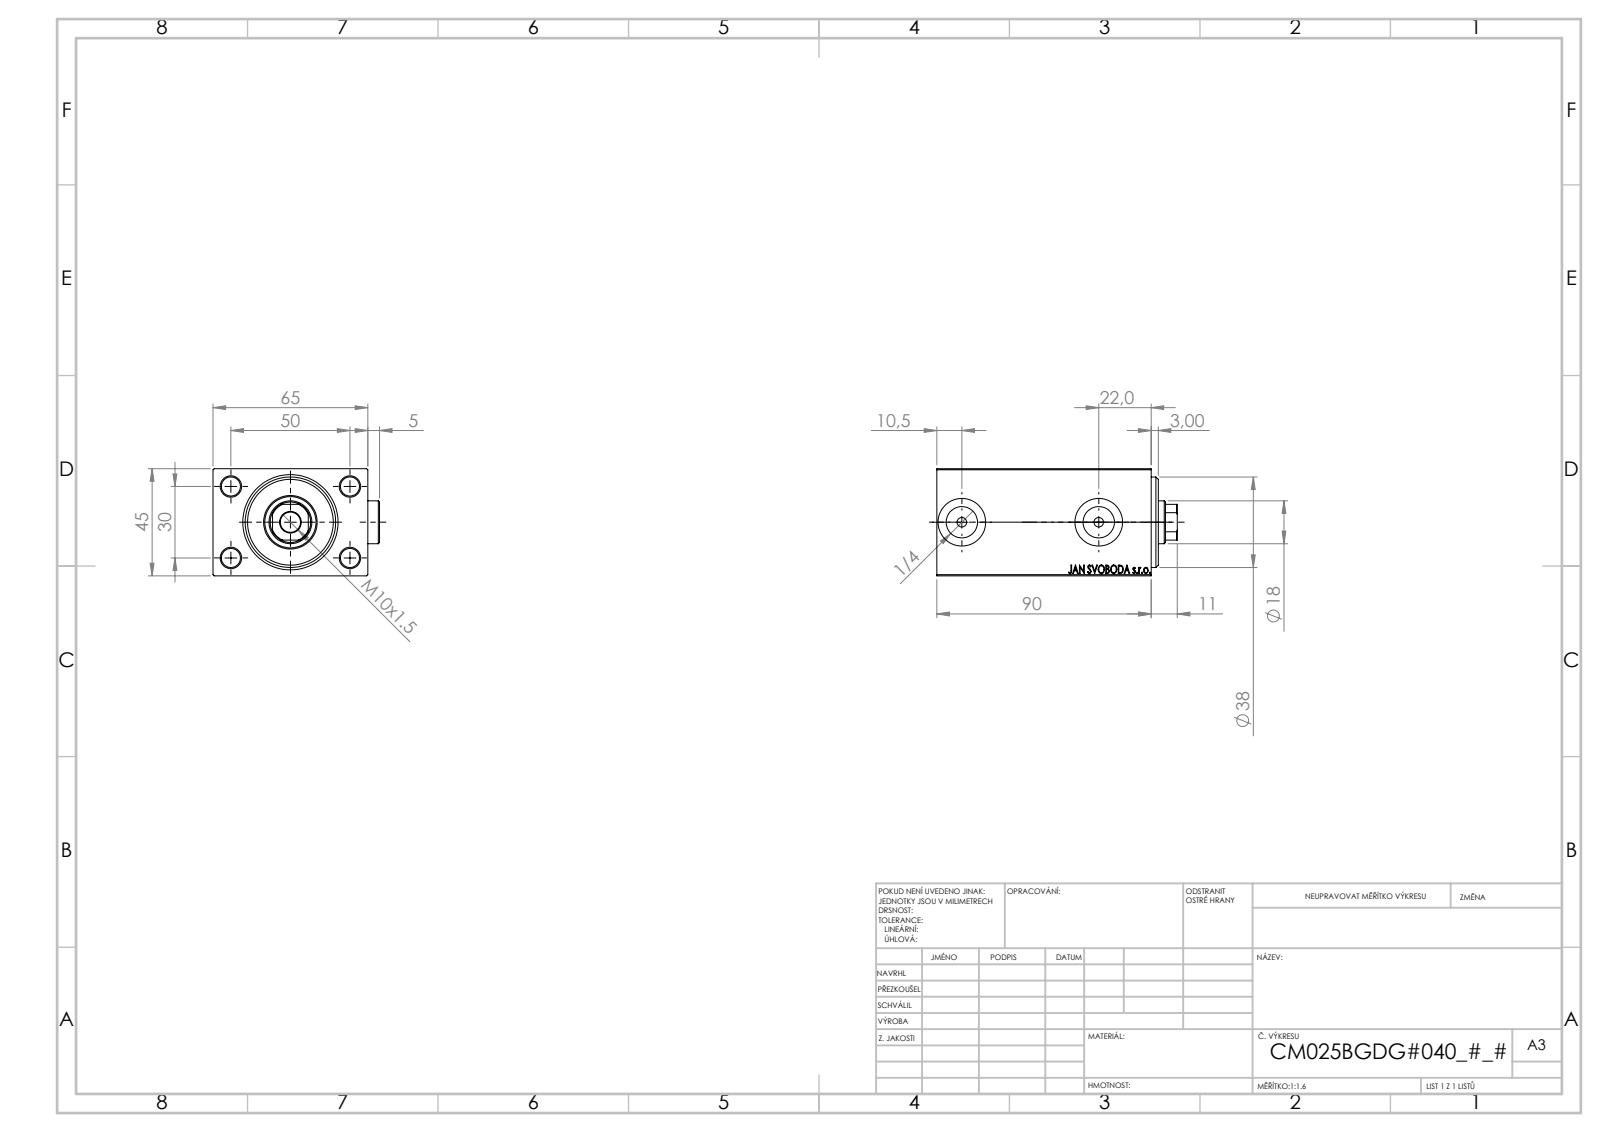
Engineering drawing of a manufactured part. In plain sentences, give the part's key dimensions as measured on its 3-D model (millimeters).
The part is named "Zatka_OIL_PORT; V450CM_B_Body; V450CM_VC_B; V450CM_B_VCP". Its 3-D file was written by "SolidWorks 2019 (CONFIG_CONTROL_DESIGN)". It is 5 solids with 935 faces: 435 planar, 70 cylindrical and 430 other. Overall it measures 101 by 69.9 by 45 millimeters. Its volume is 246 107 cubic millimeters and its surface area 50 987 square millimeters. Round holes: 4 of diameter 8, 2 of diameter 4, 2 of diameter 13.16, 2 of diameter 20, 1 of diameter 8.5, 1 of diameter 18, 1 of diameter 21.5, 1 of diameter 22.5, 1 of diameter 25, 1 of diameter 27, 1 of diameter 38. Round bosses or shafts: 2 of diameter 18. Partial cylindrical surfaces (rounded edges, fillets, slot ends): 1 of radius 8.5. The main face-to-face distances are 45, 65, 5, 6, 90, 79, 64.9, 85, 84, 8. The hole center spacings are 29.15, 30, 50, 58.31, 57.5.
